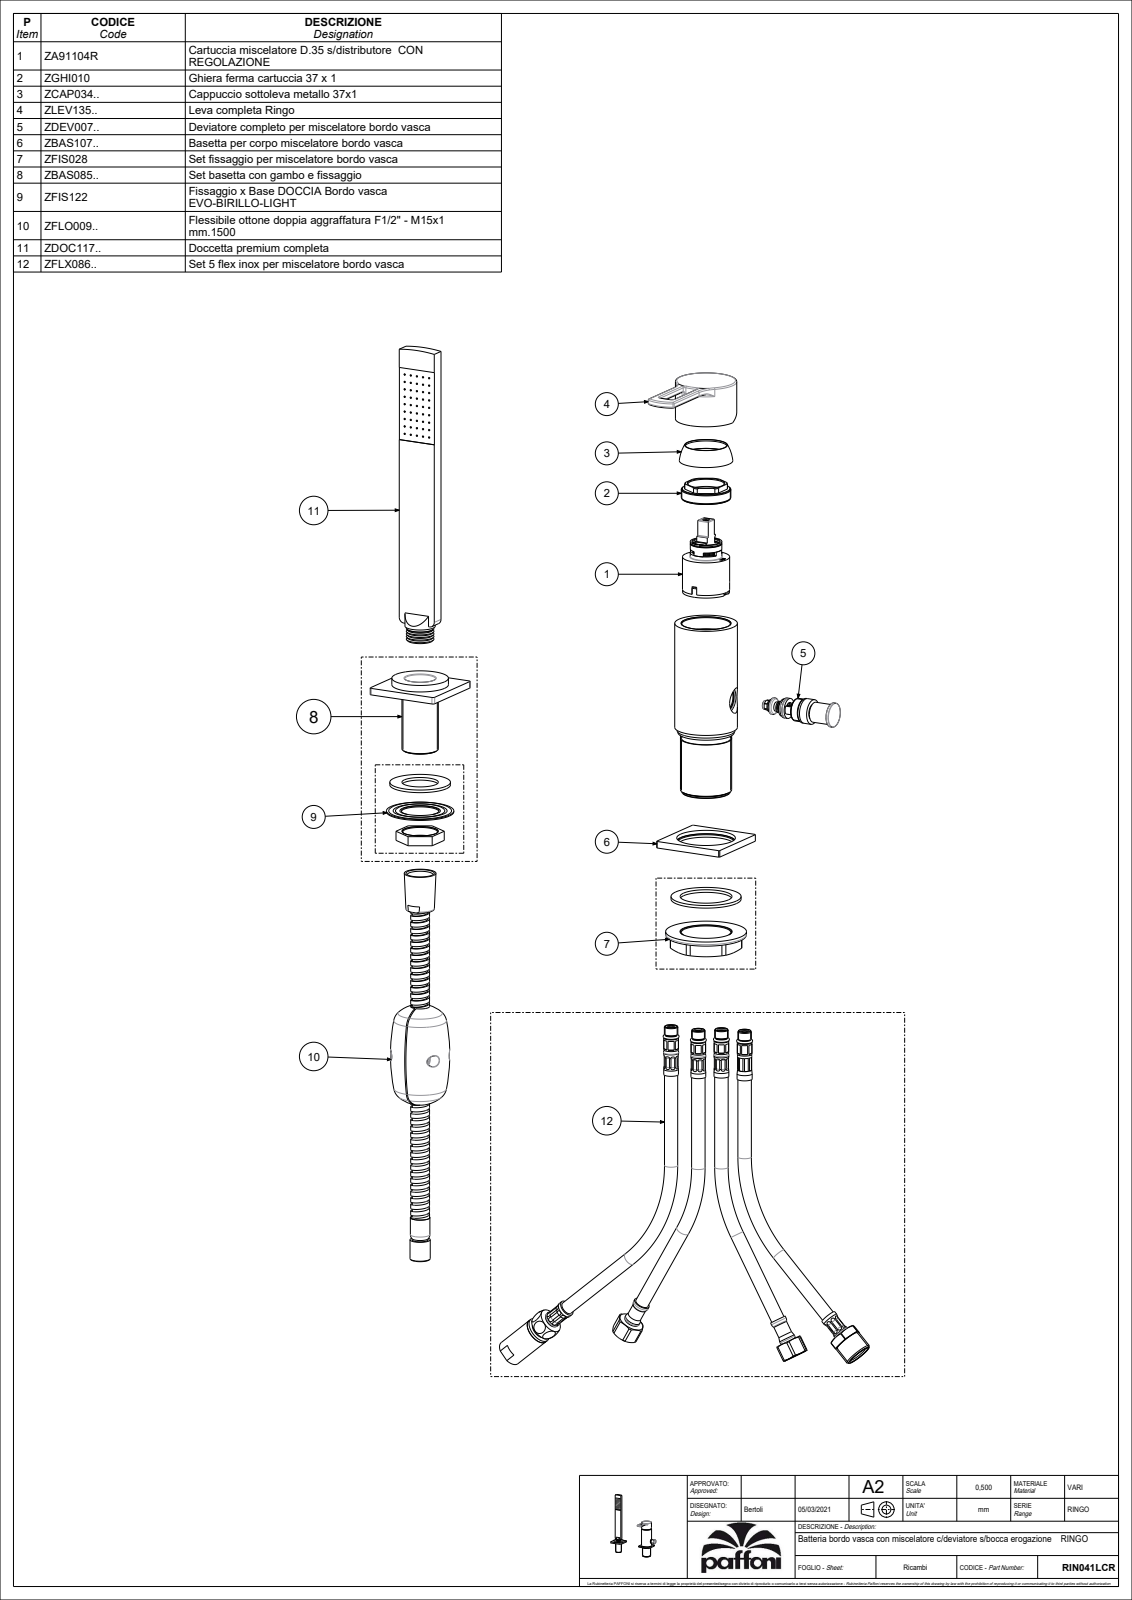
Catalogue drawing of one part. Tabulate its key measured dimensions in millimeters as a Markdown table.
| quantity | value |
| --- | --- |
| part name | RIN041LCR |
| STEP written by | CREO PARAMETRIC BY PTC INC, 2020044 (CONFIG_CONTROL_DESIGN) |
| units | millimeters |
| bodies | 4 solids, 1572 faces (908 planar, 377 cylindrical, 287 other) |
| overall size | 228 × 221.46 × 97.45 |
| volume | 228 658 mm³ |
| surface area | 97 459 mm² |
| round holes (diameter × count) | 7 × 6, 4 × 2, 3 × 1, 3.1 × 1, 3.3 × 1, 4.3 × 1, 4.5 × 1, 5 × 1, 6 × 1, 7.2 × 1, 7.8 × 1, 9 × 1 |
| round bosses / shafts (diameter × count) | 2 × 11, 46.5 × 1, 45.5 × 1, 44.2 × 1, 43 × 1, 42.5 × 1, 42 × 1, 38 × 1 |
| partial cylindrical surfaces (radius × count) | 0.5 × 34, 1 × 14, 0.15 × 11, 0.3 × 4, 1.5 × 4, 1.3 × 2, 2 × 2, 4 × 2 |
| main face-to-face distances | 10, 5, 3, 30, 1, 9.8, 1.2, 7, 8.8, 0.5 |
| hole center spacings | 3, 8.6, 10.63, 14, 14.32, 11, 59.31, 143.09 |
